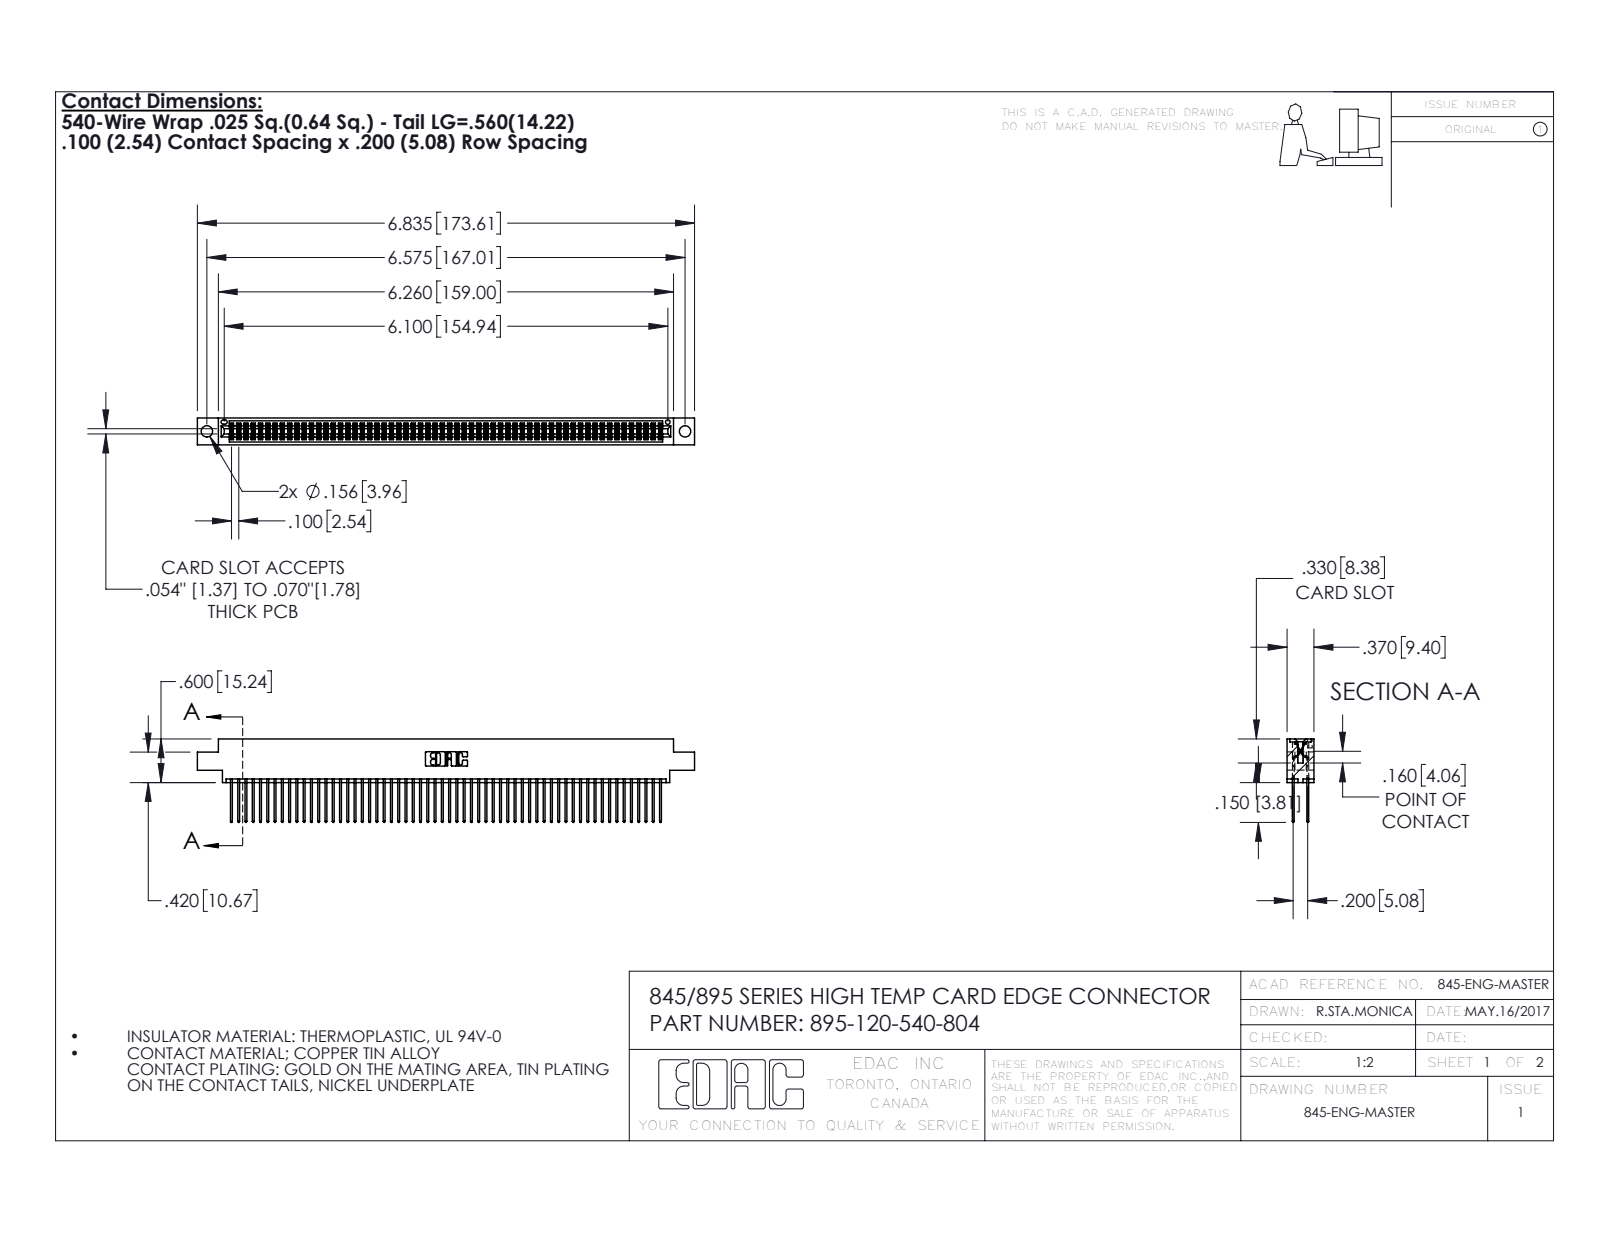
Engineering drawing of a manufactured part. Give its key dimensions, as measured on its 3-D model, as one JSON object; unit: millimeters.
{"part_name": "345-292-001_345-293-140; 345 Part_0.170 Offset - 0.156 Dia-TH; 395-120-540-804", "step_written_by": "SolidWorks 2016 (CONFIG_CONTROL_DESIGN)", "units": "millimeters", "bodies": {"solids": 121, "faces": 6130, "planar": 4044, "cylindrical": 2086, "other": 0}, "overall_size": [173.6, 29.1, 9.4], "volume_mm3": 17290, "surface_area_mm2": 27970, "round_holes": [[4, 2], [1.6, 1]], "partial_cylinders_radius": [[0.2, 180], [0.3, 120], [0.3, 22], [0.2, 6], [0.8, 6], [0.7, 3], [0.4, 2], [0.5, 2]], "face_to_face_distances": [1.8, 7.6, 5.1, 2.5, 6.9, 0.6, 9.4, 5.7, 4.4, 3.8], "hole_center_spacings": [6.9, 161, 167]}
